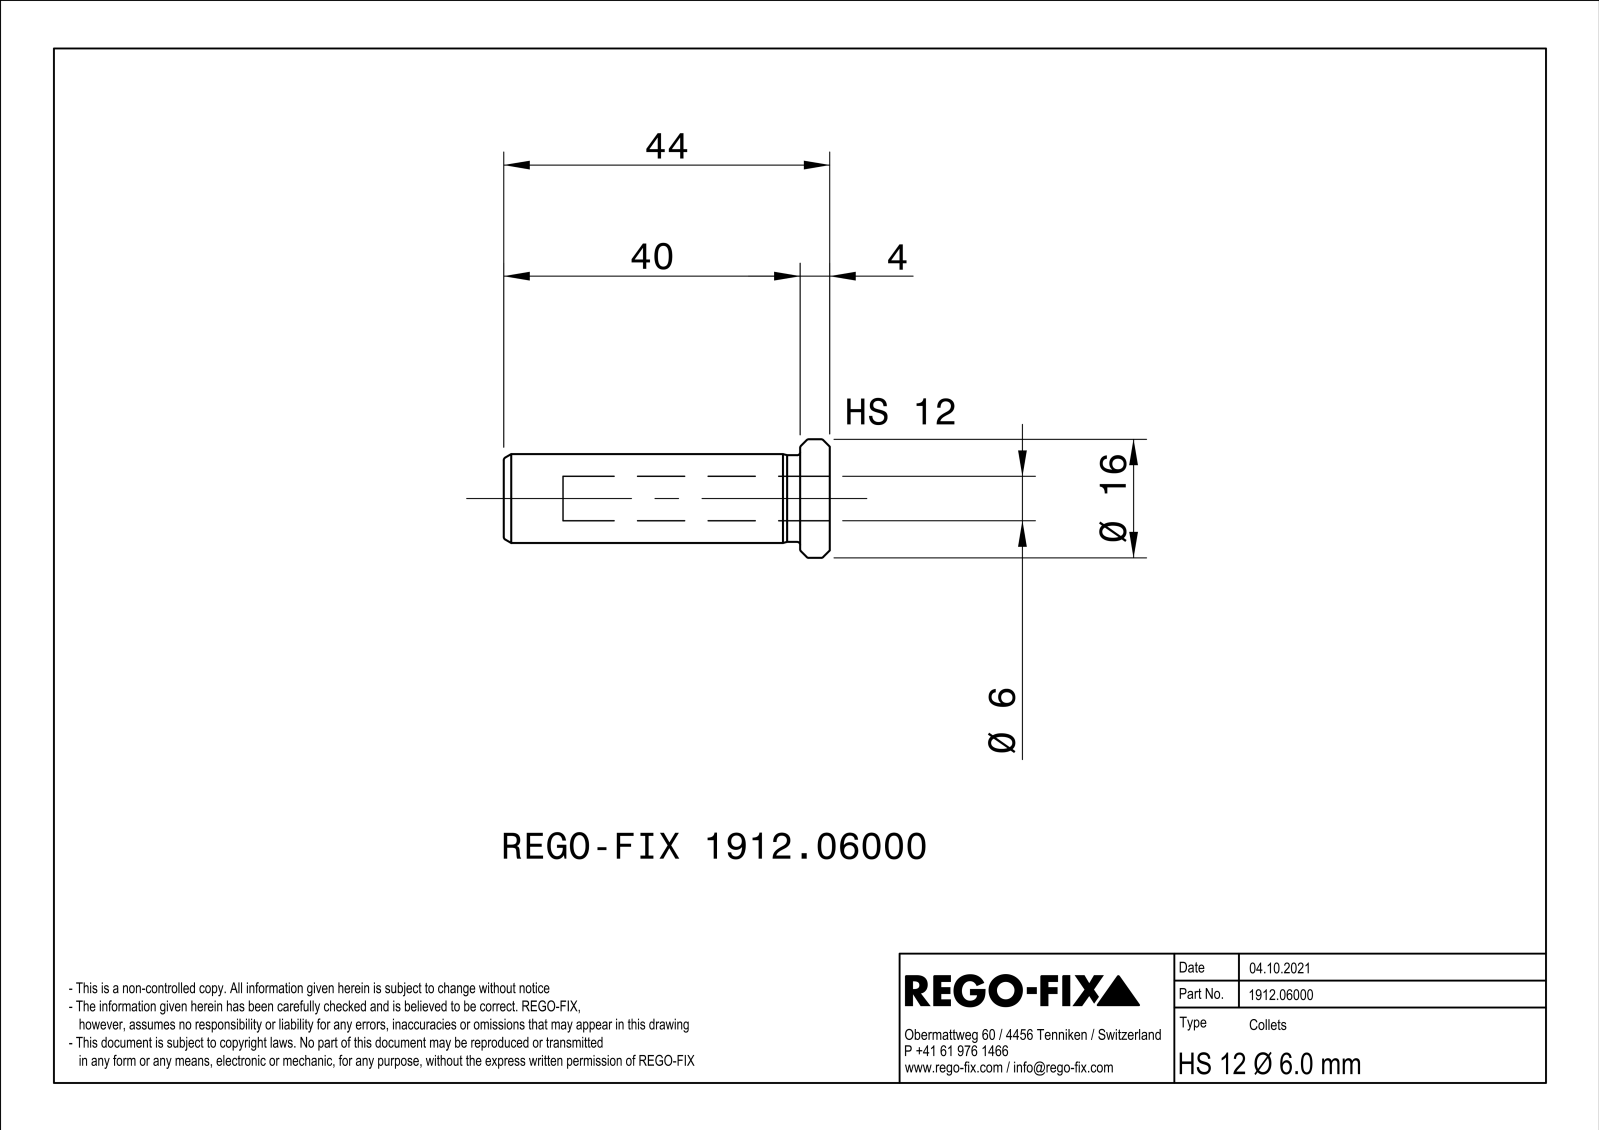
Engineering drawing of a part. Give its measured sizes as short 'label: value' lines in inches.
name: NOCUT
written by: SIEMENS PLM Software Solid Edge ST10 (AUTOMOTIVE_DESIGN)
unit: in
bodies: 1 solid, 97 faces (35 planar, 24 cylindrical, 38 other)
size: 1.732 × 0.629 × 0.629
volume: 0.217 in³; area: 5.33 in²
holes: 1× ⌀0.236, 1× ⌀0.295
bosses: 1× ⌀0.63, 1× ⌀0.472, 1× ⌀0.47, 1× ⌀0.461
face distances: 0.031, 1.732, 0.157, 1.575, 1.355, 1.197, 0.378, 0.91, 0.752, 0.445
